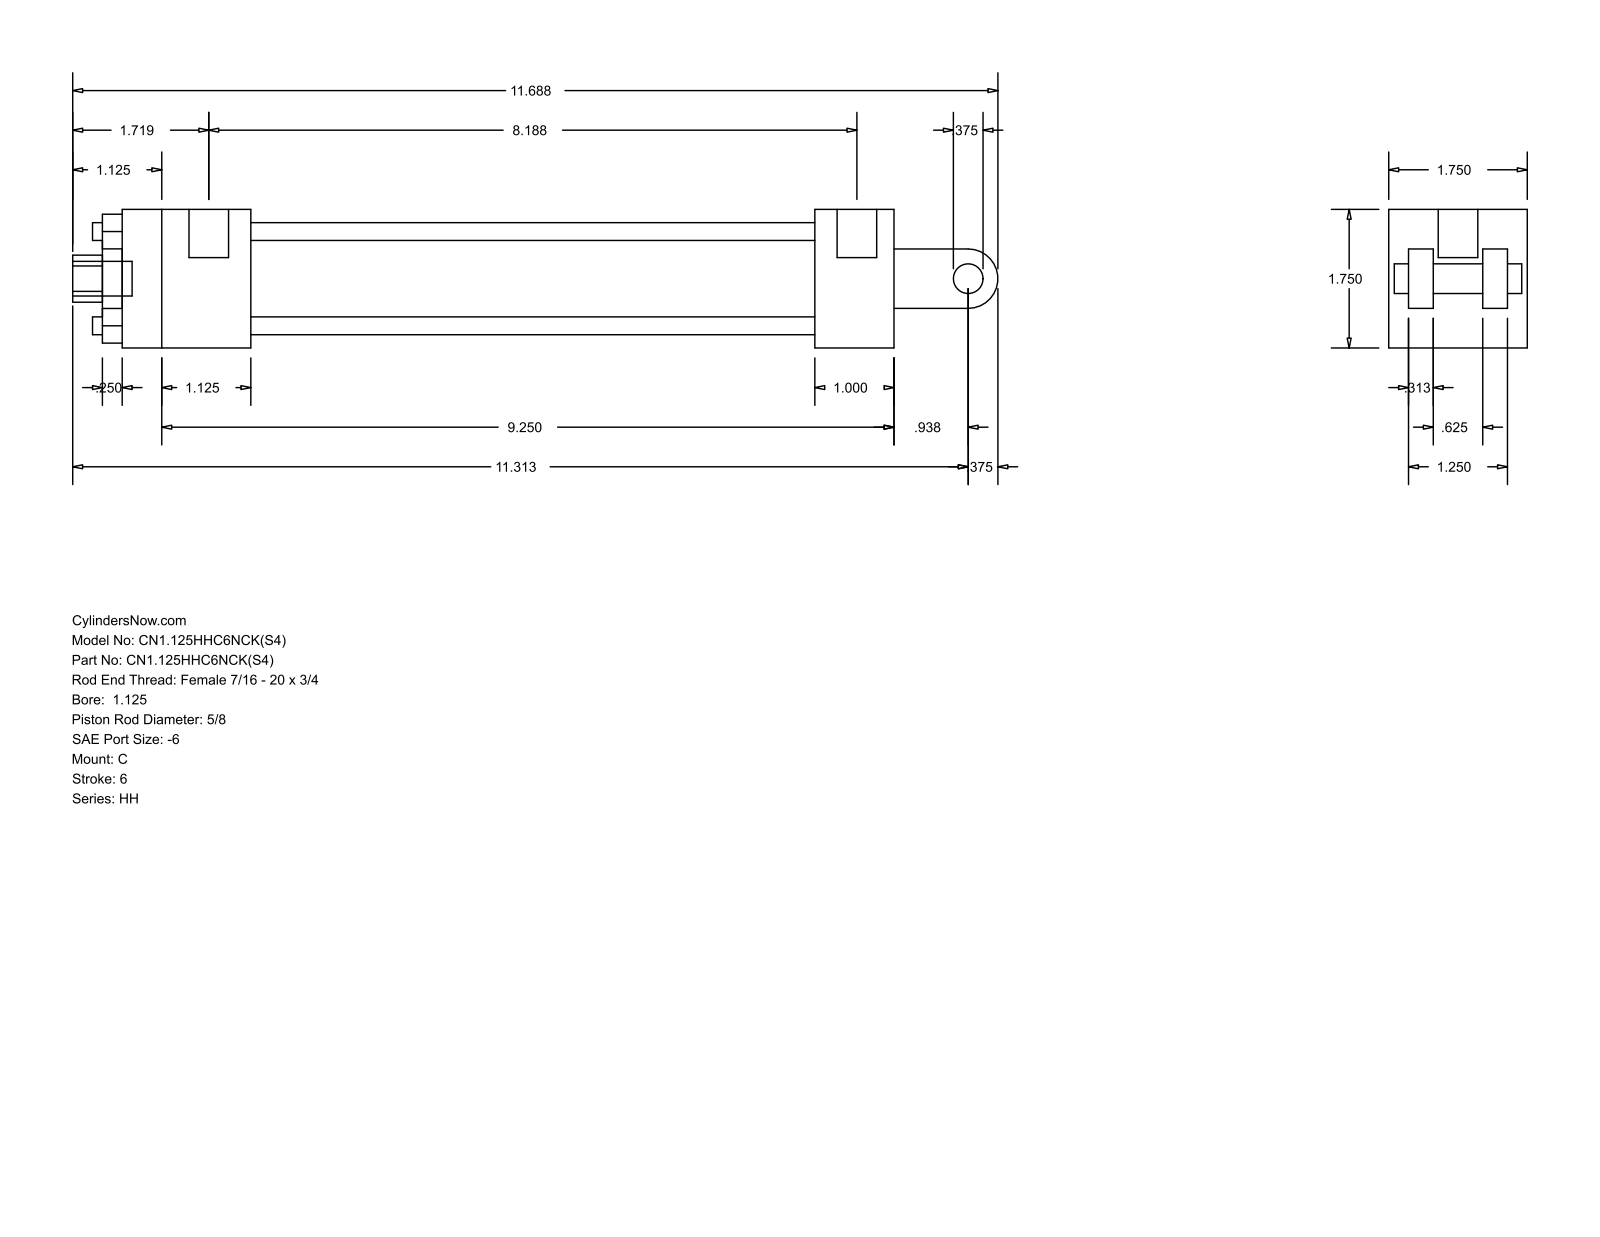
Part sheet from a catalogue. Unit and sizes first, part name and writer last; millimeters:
Units: millimetres
Overall size (bounding box): 296.86 × 44.45 × 44.45
Round holes (diameter × count): ⌀5.71 ×4, ⌀5.56 ×2, ⌀12.7 ×1, ⌀15.88 ×1, ⌀28.57 ×1, ⌀34.92 ×1
Round bosses / shafts (diameter × count): ⌀5.56 ×2, ⌀12.7 ×1, ⌀11.11 ×1, ⌀9.53 ×1
Partial cylindrical surfaces — rounded edges, fillets, slot ends (radius × count): R7.54 ×1, R9.53 ×1
Main face-to-face distances: 44.46, 6.35, 31.76, 14.29, 12.7, 30.17, 38.11, 7.94, 23.82, 25.4
Hole centre spacings: 21.37, 30.22, 42.74
Bodies: 0 solids, 99 faces (70 planar, 29 cylindrical, 0 other)
Part name (STEP PRODUCT): HH_C__0112_0.625
STEP written by: GSSL Pune (CONFIG_CONTROL_DESIGN)
